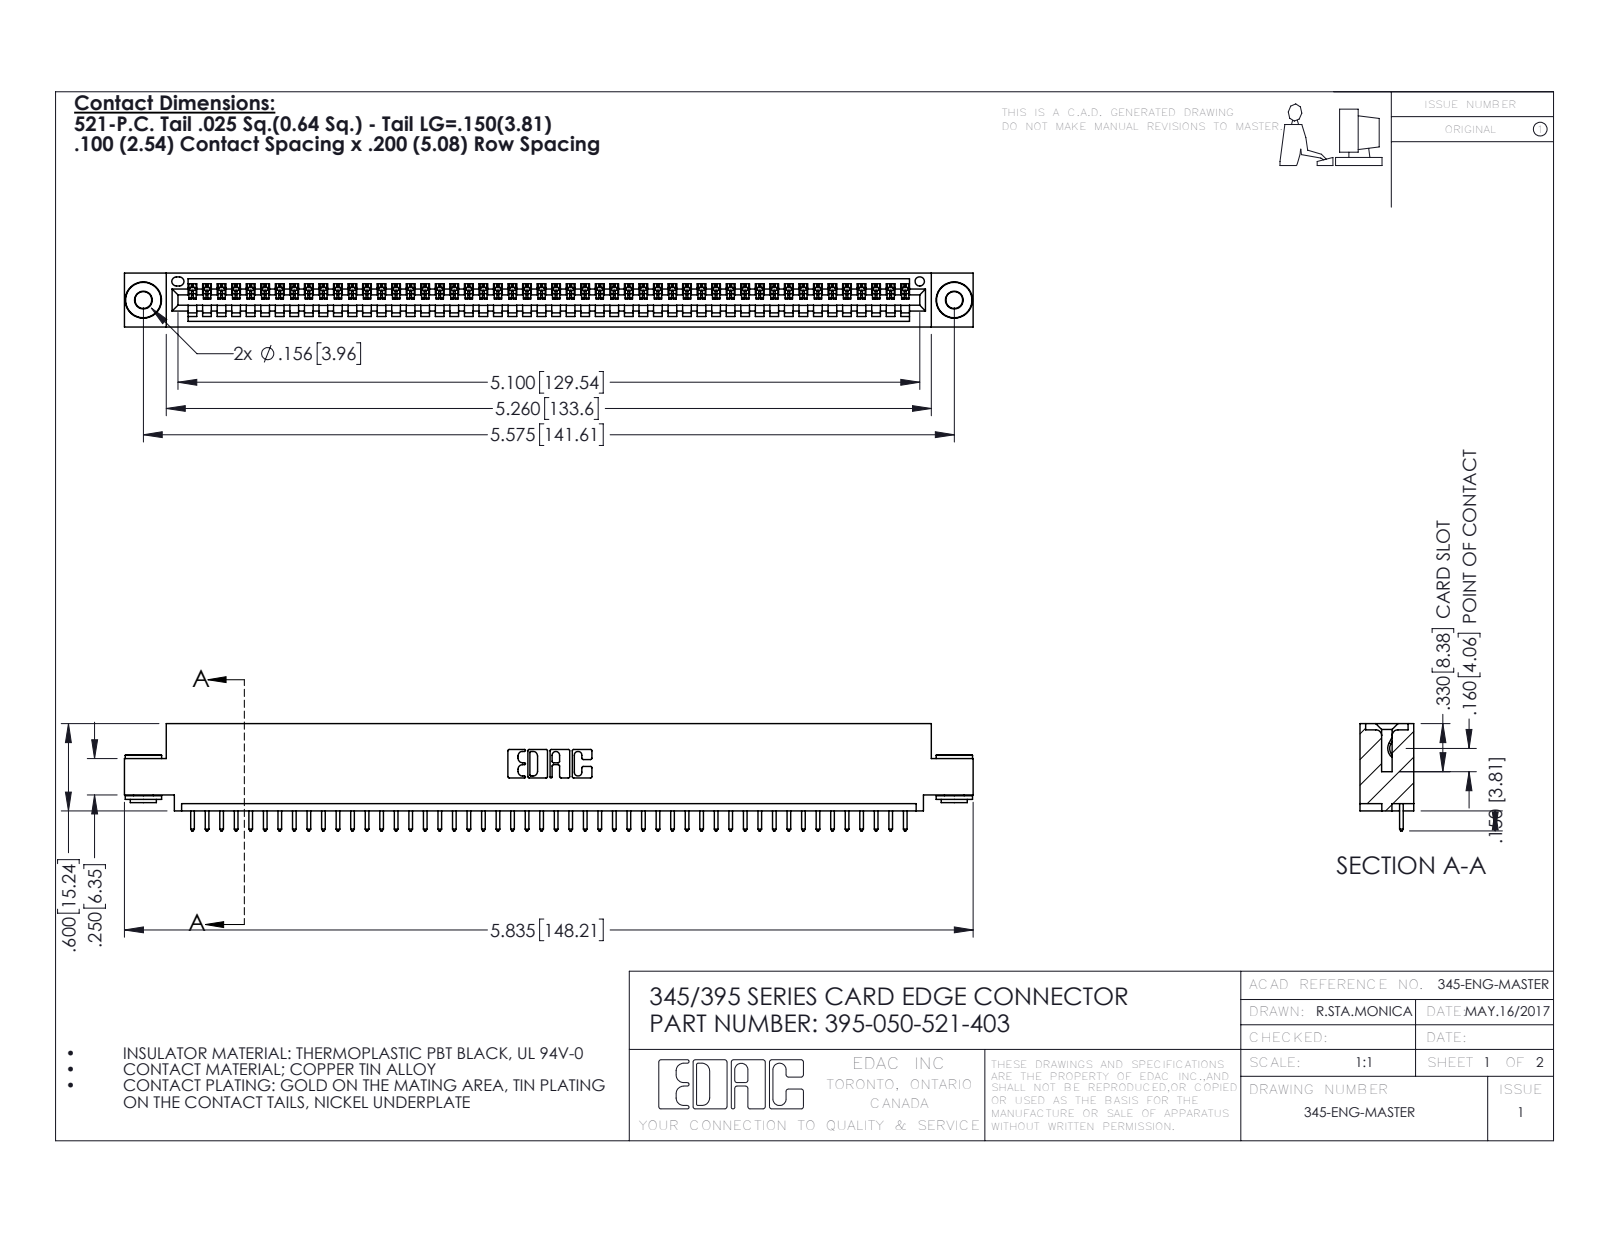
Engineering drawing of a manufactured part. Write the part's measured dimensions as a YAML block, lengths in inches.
part_name: "345 Part_0.110 Offset - 0.156 Dia-TH; 345-292-001_345-293-121; 395-050-521-403; 345-250-002_345-250-002-102"
step_written_by: "SolidWorks 2016 (CONFIG_CONTROL_DESIGN)"
units: inches
bodies: {solids: 53, faces: 3068, planar: 2094, cylindrical: 966, other: 8}
overall_size: [5.835, 0.737, 0.37]
volume: 0.851
surface_area: 28.49
round_holes:
  - {diameter: 0.116, count: 2}
  - {diameter: 0.156, count: 2}
  - {diameter: 0.064, count: 1}
round_bosses_or_shafts:
  - {diameter: 0.25, count: 2}
  - {diameter: 0.18, count: 2}
  - {diameter: 0.136, count: 2}
partial_cylinders:
  - {radius: 0.006, count: 100}
  - {radius: 0.01, count: 100}
  - {radius: 0.01, count: 22}
  - {radius: 0.007, count: 6}
  - {radius: 0.031, count: 6}
  - {radius: 0.026, count: 3}
  - {radius: 0.031, count: 2}
  - {radius: 0.04, count: 2}
face_to_face_distances: [0.072, 0.298, 0.37, 0.2, 0.025, 0.098, 0.272, 0.225, 0.149, 0.072]
hole_center_spacings: [0.27, 5.339, 5.575]
